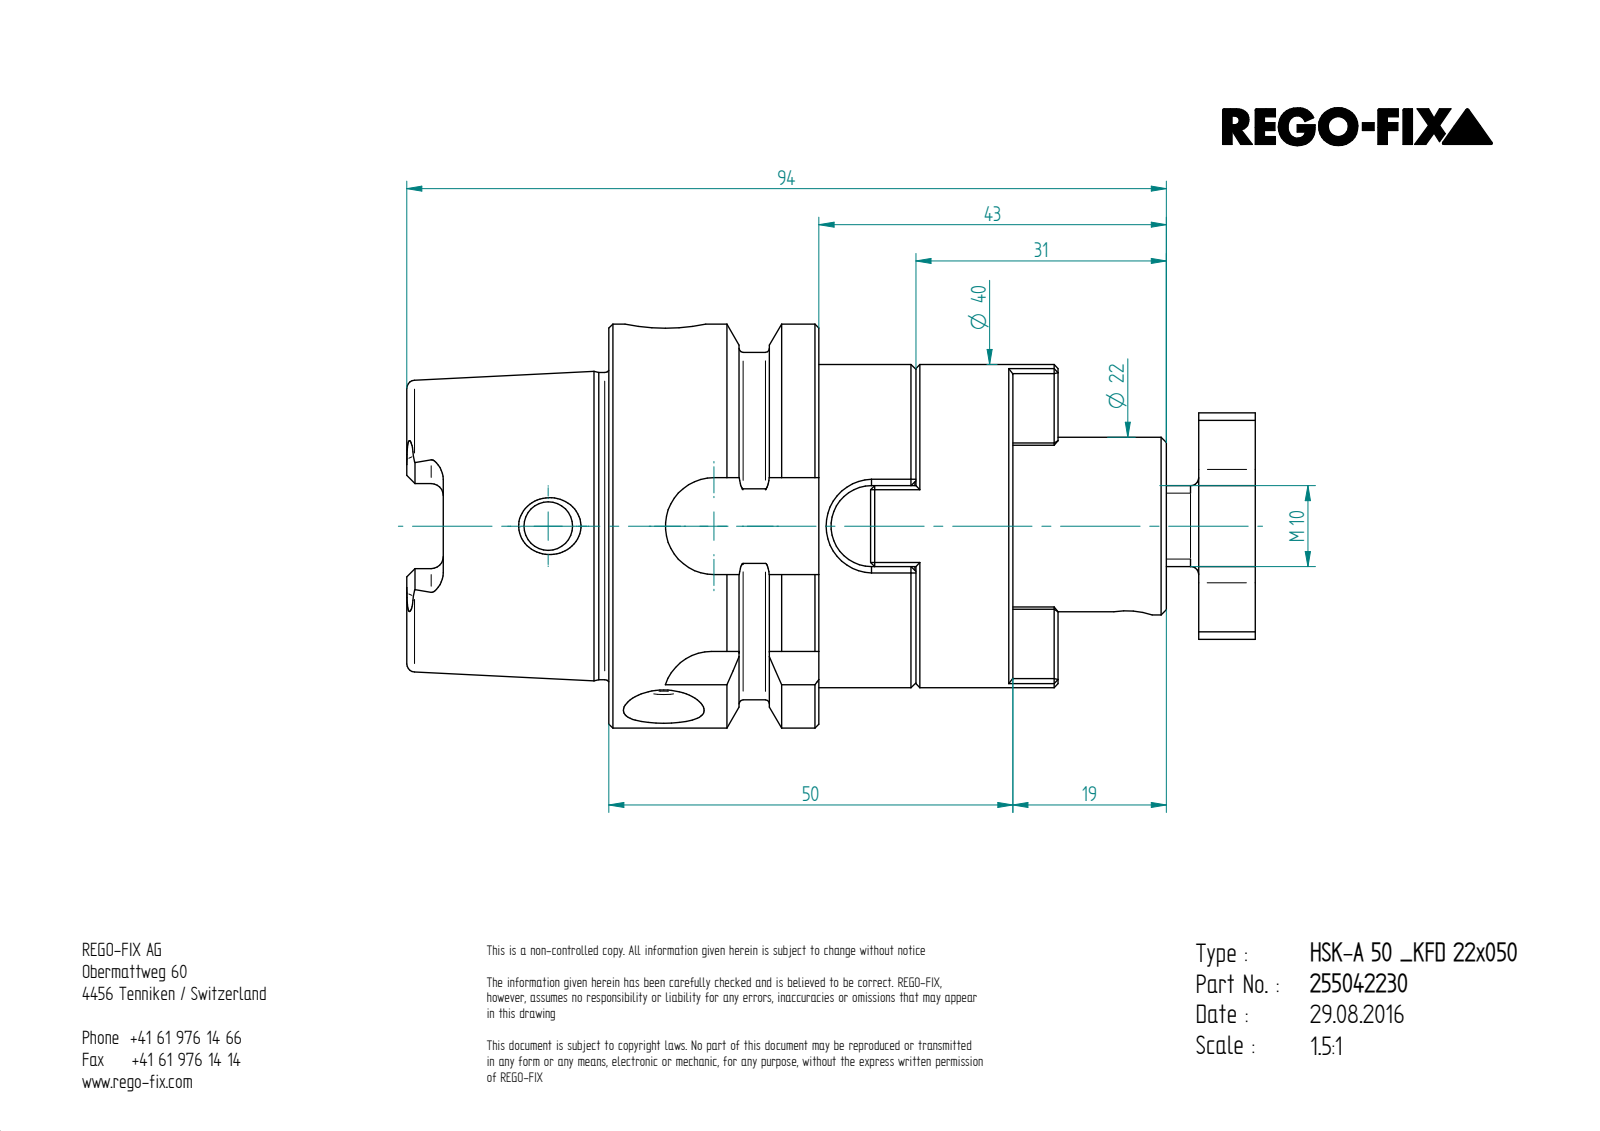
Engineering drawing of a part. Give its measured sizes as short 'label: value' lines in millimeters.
written by: Unknown (AUTOMOTIVE_DESIGN)
unit: mm
bodies: 1 solid, 261 faces (135 planar, 53 cylindrical, 73 other)
size: 105 × 50 × 50
volume: 87 926 mm³; area: 23 832 mm²
holes: 2× ⌀10, 1× ⌀5, 1× ⌀6, 1× ⌀6.8, 1× ⌀8.38, 1× ⌀10.5, 1× ⌀14.92, 1× ⌀17, 1× ⌀22, 1× ⌀26, 1× ⌀32
bosses: 1× ⌀50, 1× ⌀43, 1× ⌀40, 1× ⌀38.01, 1× ⌀21.4, 1× ⌀10
rounds: 6× R1.5, 4× R2, 4× R2.38, 4× R6, 2× R3, 1× R5, 1× R14
face distances: 26, 24, 10, 30, 50, 16, 80, 54, 35, 23
